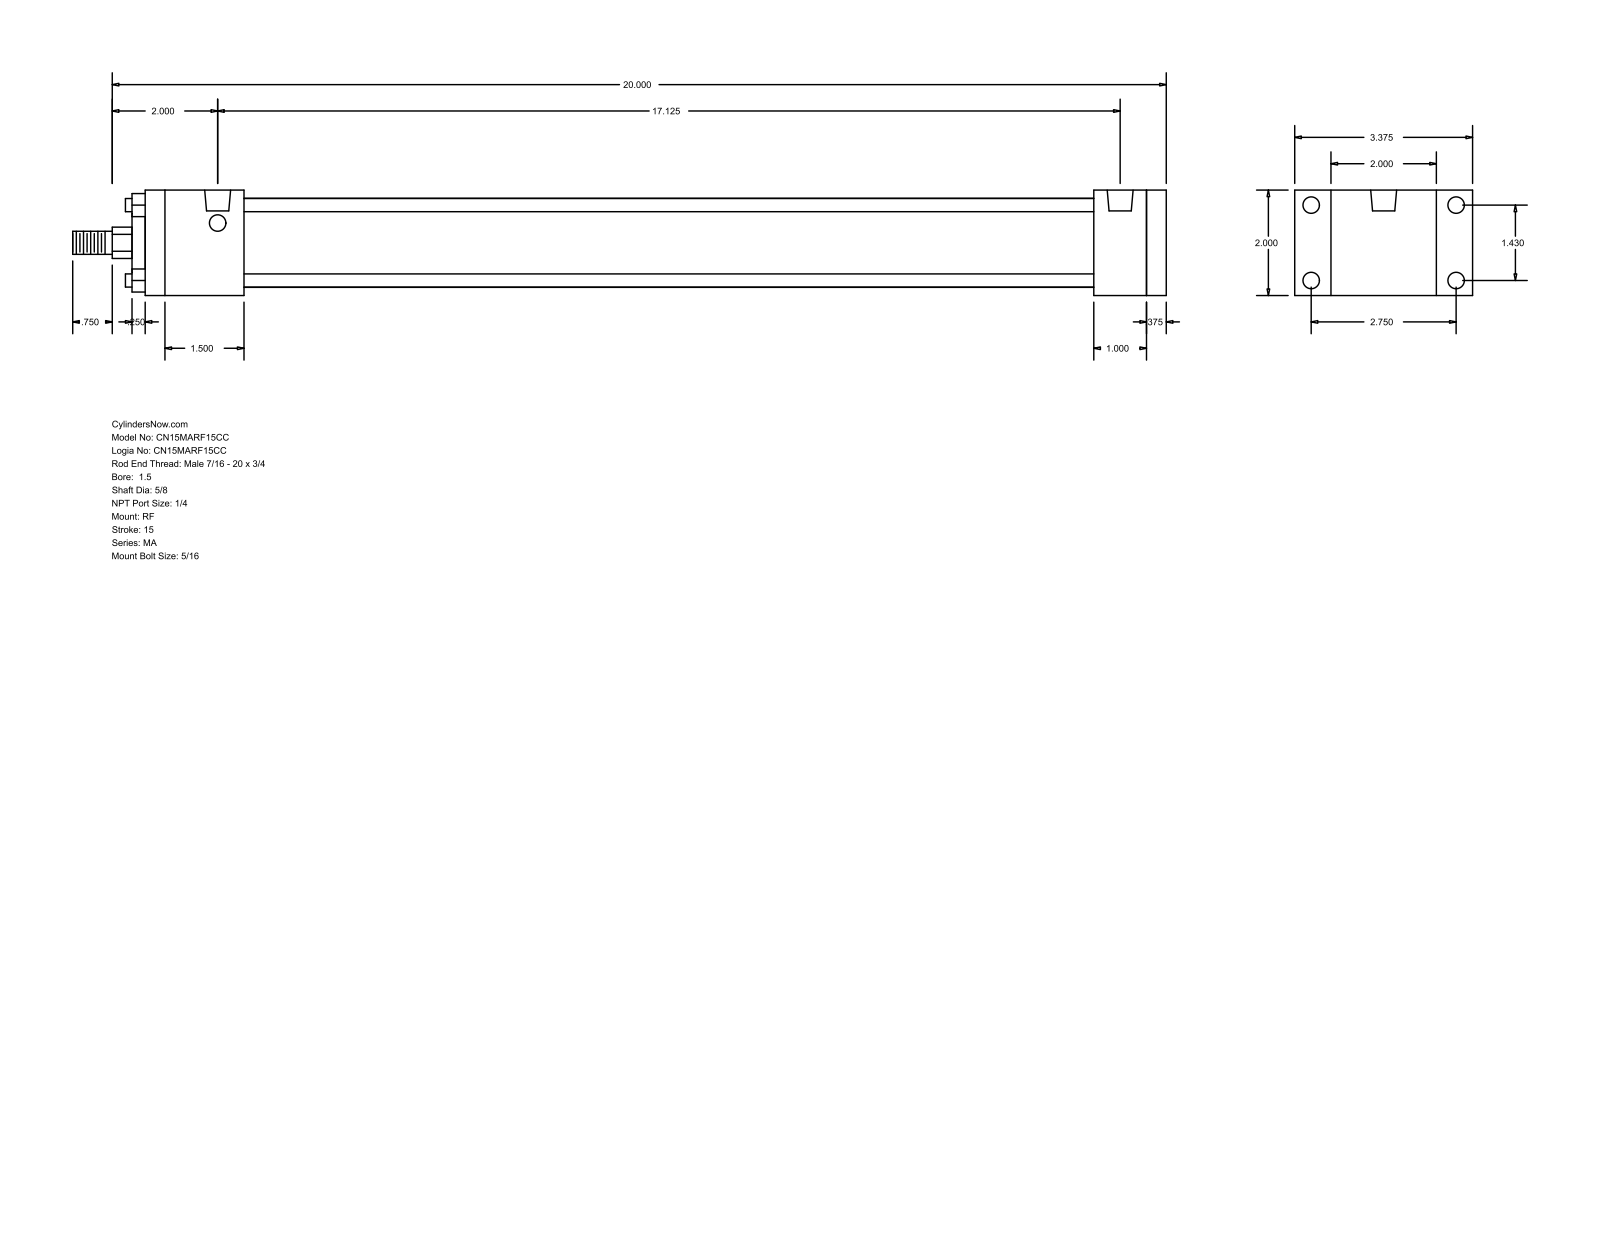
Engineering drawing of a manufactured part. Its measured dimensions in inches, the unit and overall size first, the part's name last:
Units: inches
Overall size (bounding box): 20.75 × 3.375 × 2
Round holes (diameter × count): ⌀0.313 ×8, ⌀0.492 ×2
Round bosses / shafts (diameter × count): ⌀0.25 ×4, ⌀1.69 ×1, ⌀1.125 ×1, ⌀0.625 ×1, ⌀0.437 ×1
Partial cylindrical surfaces — rounded edges, fillets, slot ends (radius × count): R0.297 ×1
Main face-to-face distances: 2, 19.375, 0.375, 19, 1.375, 18, 1, 1.875, 16.125, 17.125
Hole centre spacings: 1.43, 2.75, 3.099, 17.125
Bodies: 0 solids, 92 faces (64 planar, 28 cylindrical, 0 other)
Part name (STEP PRODUCT): MA_RF__0150_0.625
STEP written by: GSSL Pune (CONFIG_CONTROL_DESIGN)
